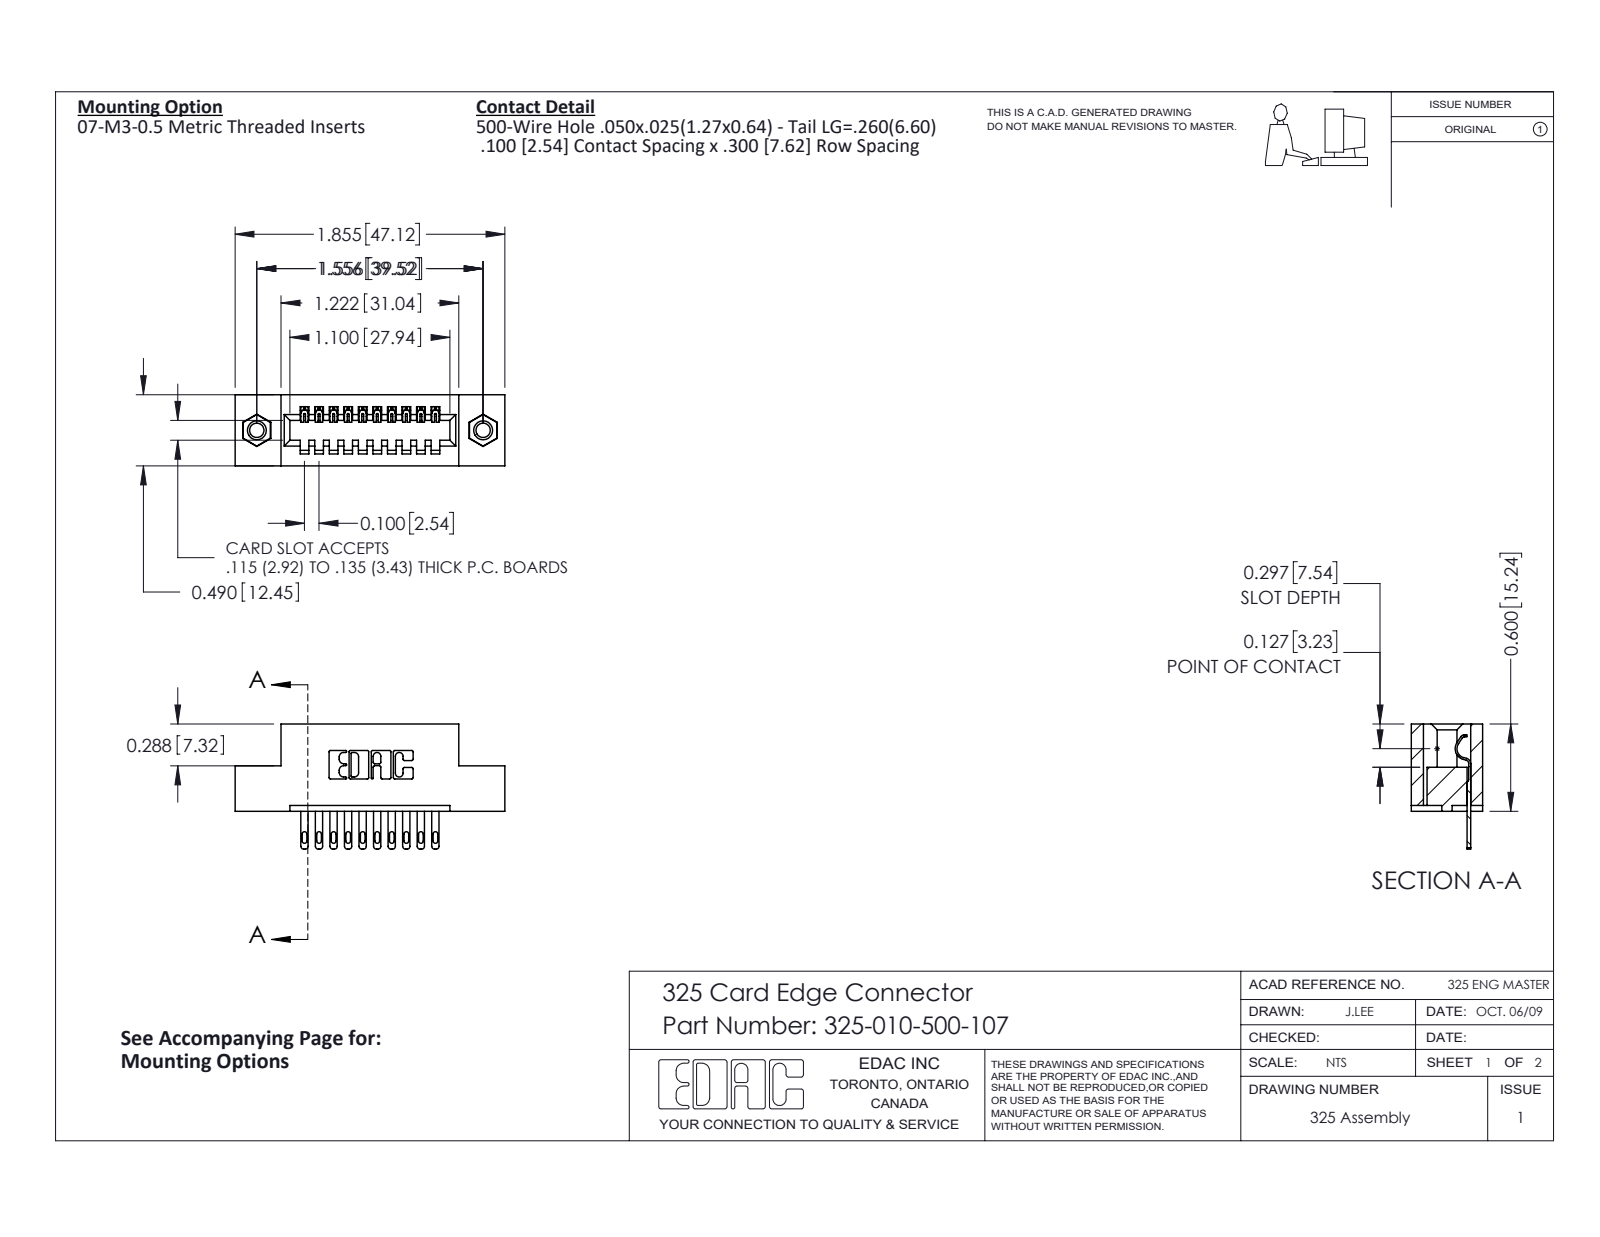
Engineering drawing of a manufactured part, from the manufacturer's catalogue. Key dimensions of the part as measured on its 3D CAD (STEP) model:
Part name (STEP PRODUCT): 325-292-001_325-293-100; 325 Part_TI; 325-010-500-107; 345-250-001_345-250-005-103
STEP written by: SolidWorks 2016 (CONFIG_CONTROL_DESIGN)
Units: inches
Bodies: 13 solids, 714 faces (462 planar, 236 cylindrical, 16 other)
Overall size (bounding box): 1.855 × 0.86 × 0.49
Volume: 0.349 in³ · Surface area: 8.927 in²
Round holes (diameter × count): ⌀0.098 ×2, ⌀0.125 ×2, ⌀0.16 ×2
Round bosses / shafts (diameter × count): ⌀0.155 ×2
Partial cylindrical surfaces — rounded edges, fillets, slot ends (radius × count): R0.01 ×22, R0.006 ×20, R0.016 ×20, R0.02 ×20, R0.007 ×6, R0.031 ×6, R0.026 ×3, R0.014 ×1
Main face-to-face distances: 0.3, 0.083, 0.407, 0.49, 0.04, 0.1, 0.2, 0.6, 0.4, 0.107
Hole centre spacings: 1.556
